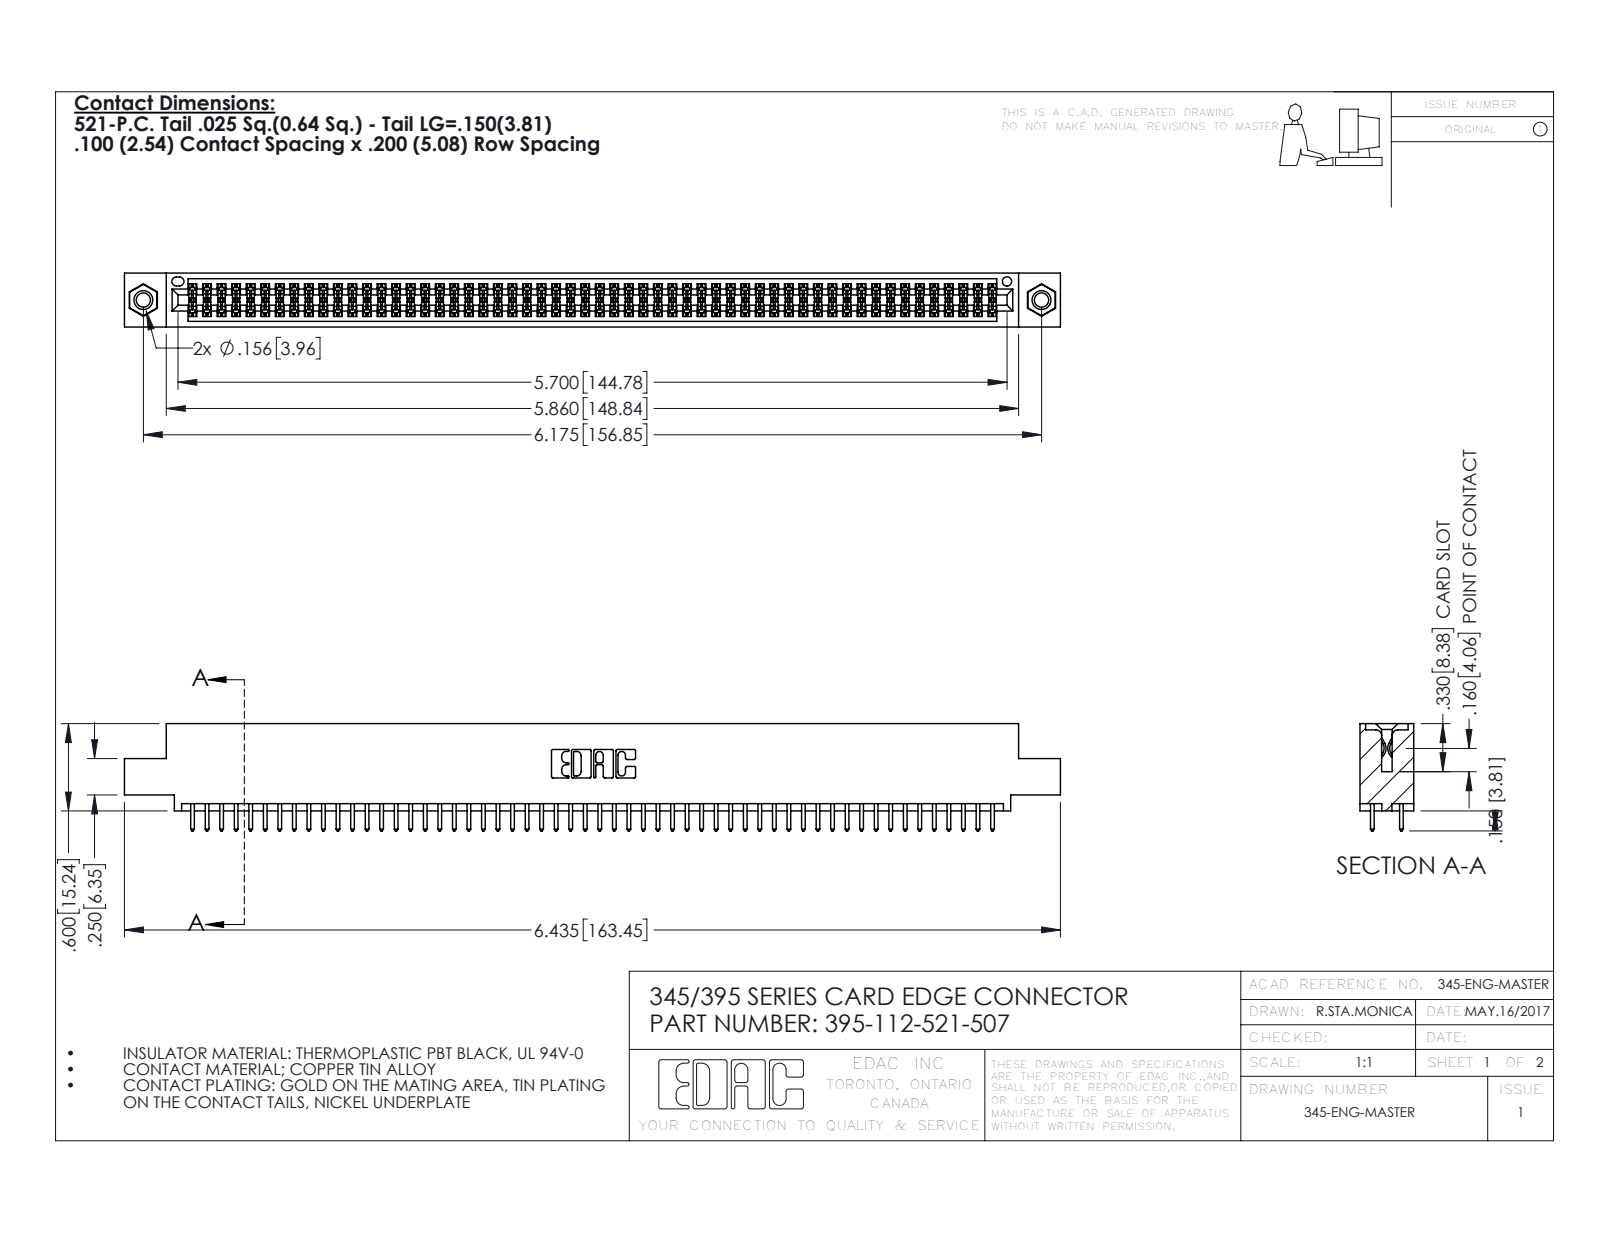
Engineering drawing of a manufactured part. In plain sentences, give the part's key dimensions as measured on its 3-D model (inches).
The part is named "395-112-521-507; 345-292-001_345-293-121; 345 Part_0.110 Offset - 0.156 Dia-TI; 345-250-001_345-250-005-103". Its 3-D file was written by "SolidWorks 2016 (CONFIG_CONTROL_DESIGN)". It is 115 solids with 5790 faces: 3812 planar, 1962 cylindrical and 16 other. Overall it measures 6.435 by 0.737 by 0.37 inches. Its volume is 0.969 cubic inches and its surface area 36.52 square inches. Round holes: 2 of diameter 0.098, 2 of diameter 0.125, 2 of diameter 0.156, 1 of diameter 0.064. Round bosses or shafts: 2 of diameter 0.155. Partial cylindrical surfaces (rounded edges, fillets, slot ends): 168 of radius 0.006, 112 of radius 0.01, 22 of radius 0.01, 6 of radius 0.007, 6 of radius 0.031, 3 of radius 0.026, 2 of radius 0.014, 2 of radius 0.019. The main face-to-face distances are 0.072, 0.298, 0.2, 0.098, 0.272, 0.025, 0.37, 0.225, 0.175, 0.149. The hole center spacings are 0.27, 5.939, 6.175.
